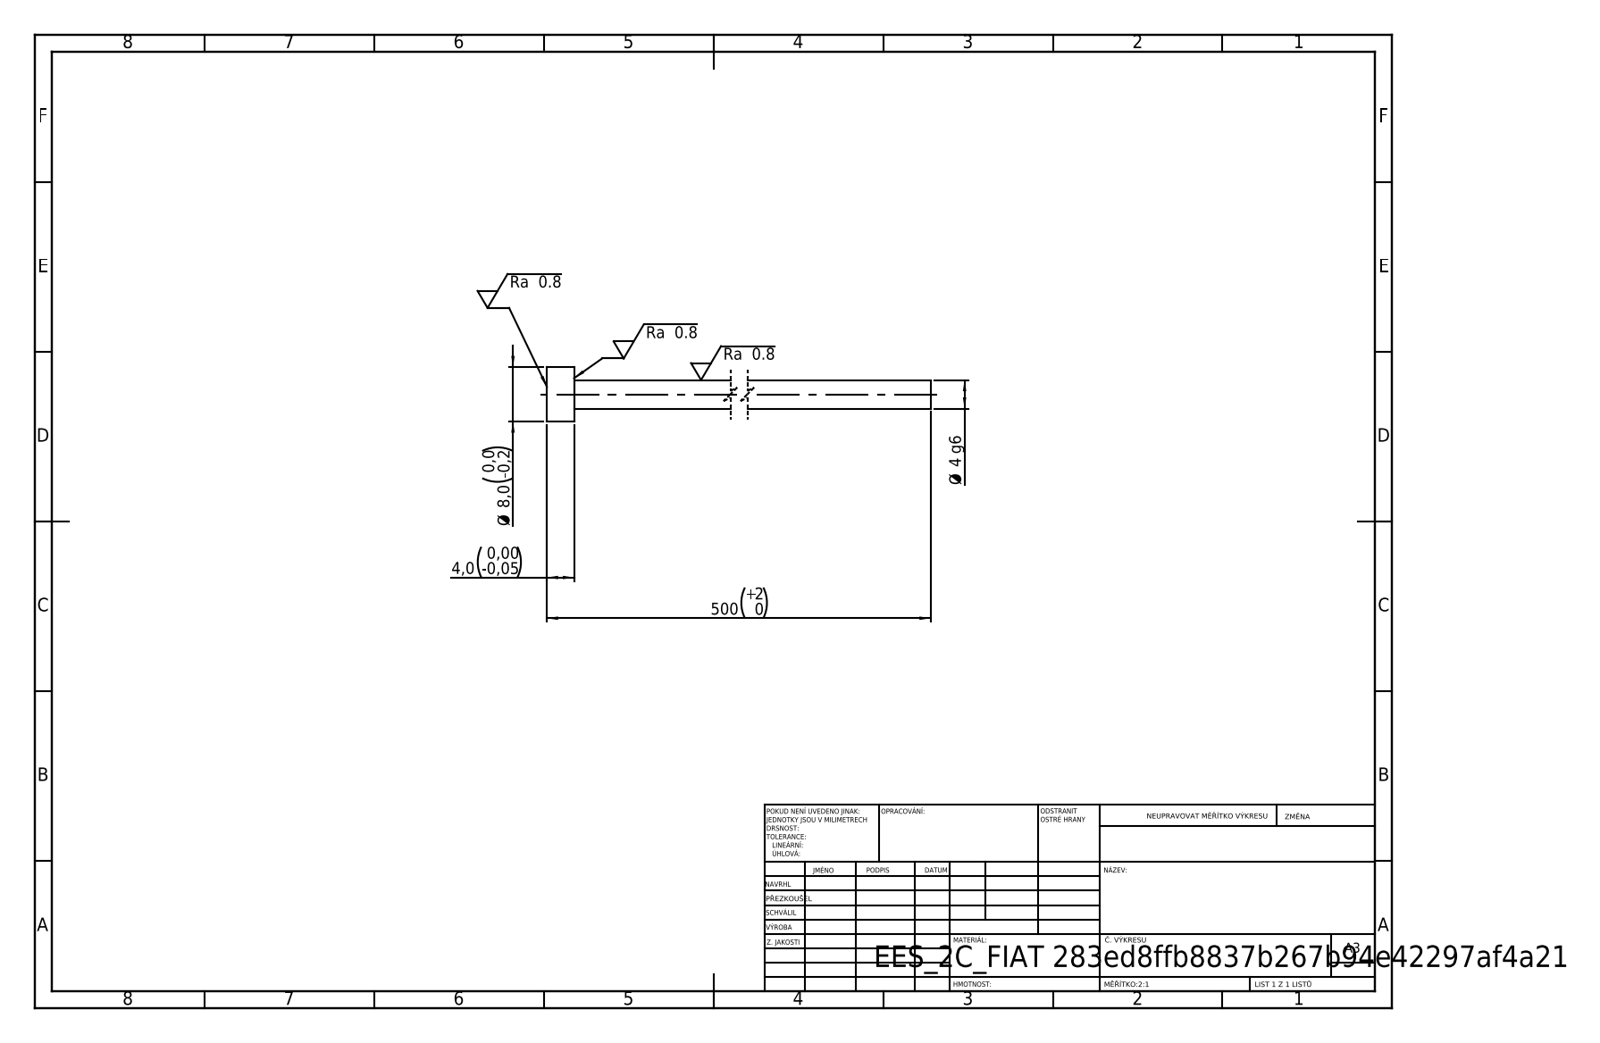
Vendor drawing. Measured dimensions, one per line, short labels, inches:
written by: SolidWorks 2019 (CONFIG_CONTROL_DESIGN)
unit: in
bodies: 1 solid, 7 faces (3 planar, 4 cylindrical, 0 other)
size: 19.685 × 0.315 × 0.315
volume: 0.432 in³; area: 10.46 in²
bosses: 1× ⌀0.315, 1× ⌀0.165
face distances: 0.157, 19.685, 19.528
